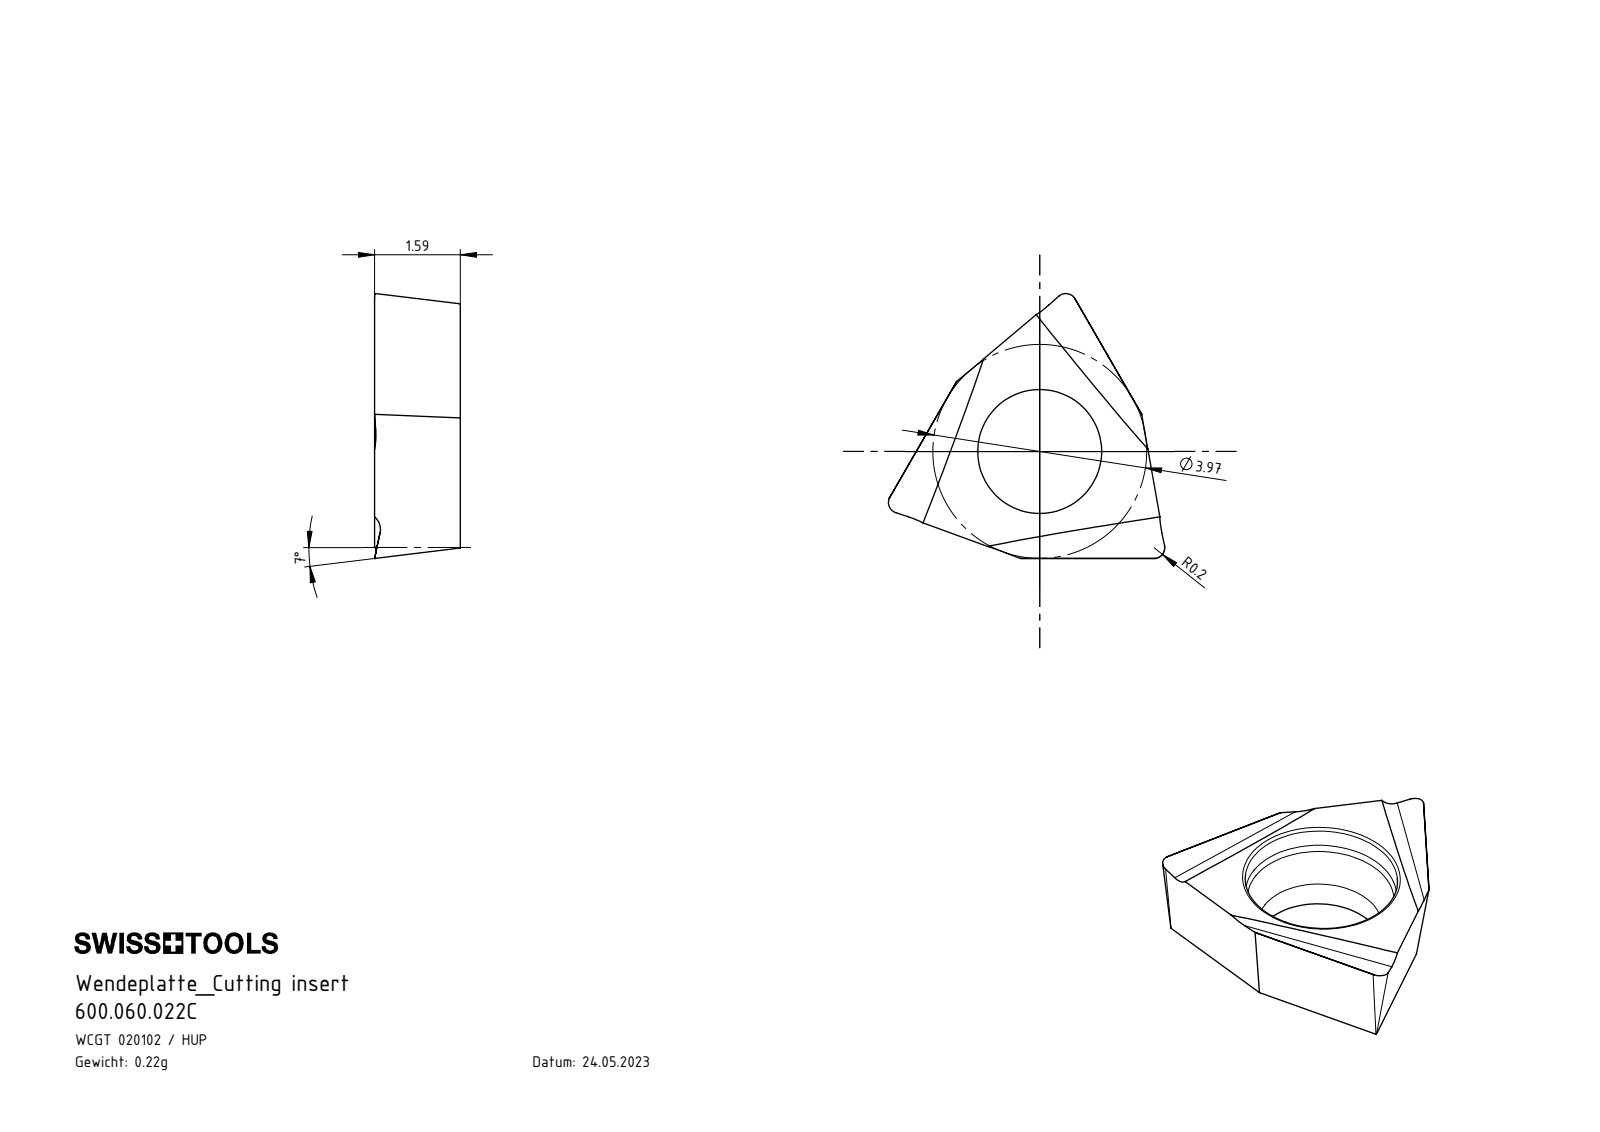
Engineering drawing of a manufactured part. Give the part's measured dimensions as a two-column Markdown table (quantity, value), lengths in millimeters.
| quantity | value |
| --- | --- |
| part name | 600.060.022C |
| STEP written by | SolidWorks 2022 (AUTOMOTIVE_DESIGN) |
| units | millimeters |
| bodies | 1 solid, 31 faces (14 planar, 5 cylindrical, 12 other) |
| overall size | 5.13 × 4.92 × 1.59 |
| volume | 15 mm³ |
| surface area | 56 mm² |
| round holes (diameter × count) | 2.3 × 1 |
| partial cylindrical surfaces (radius × count) | 0.3 × 3 |
| main face-to-face distances | 1.59 |
